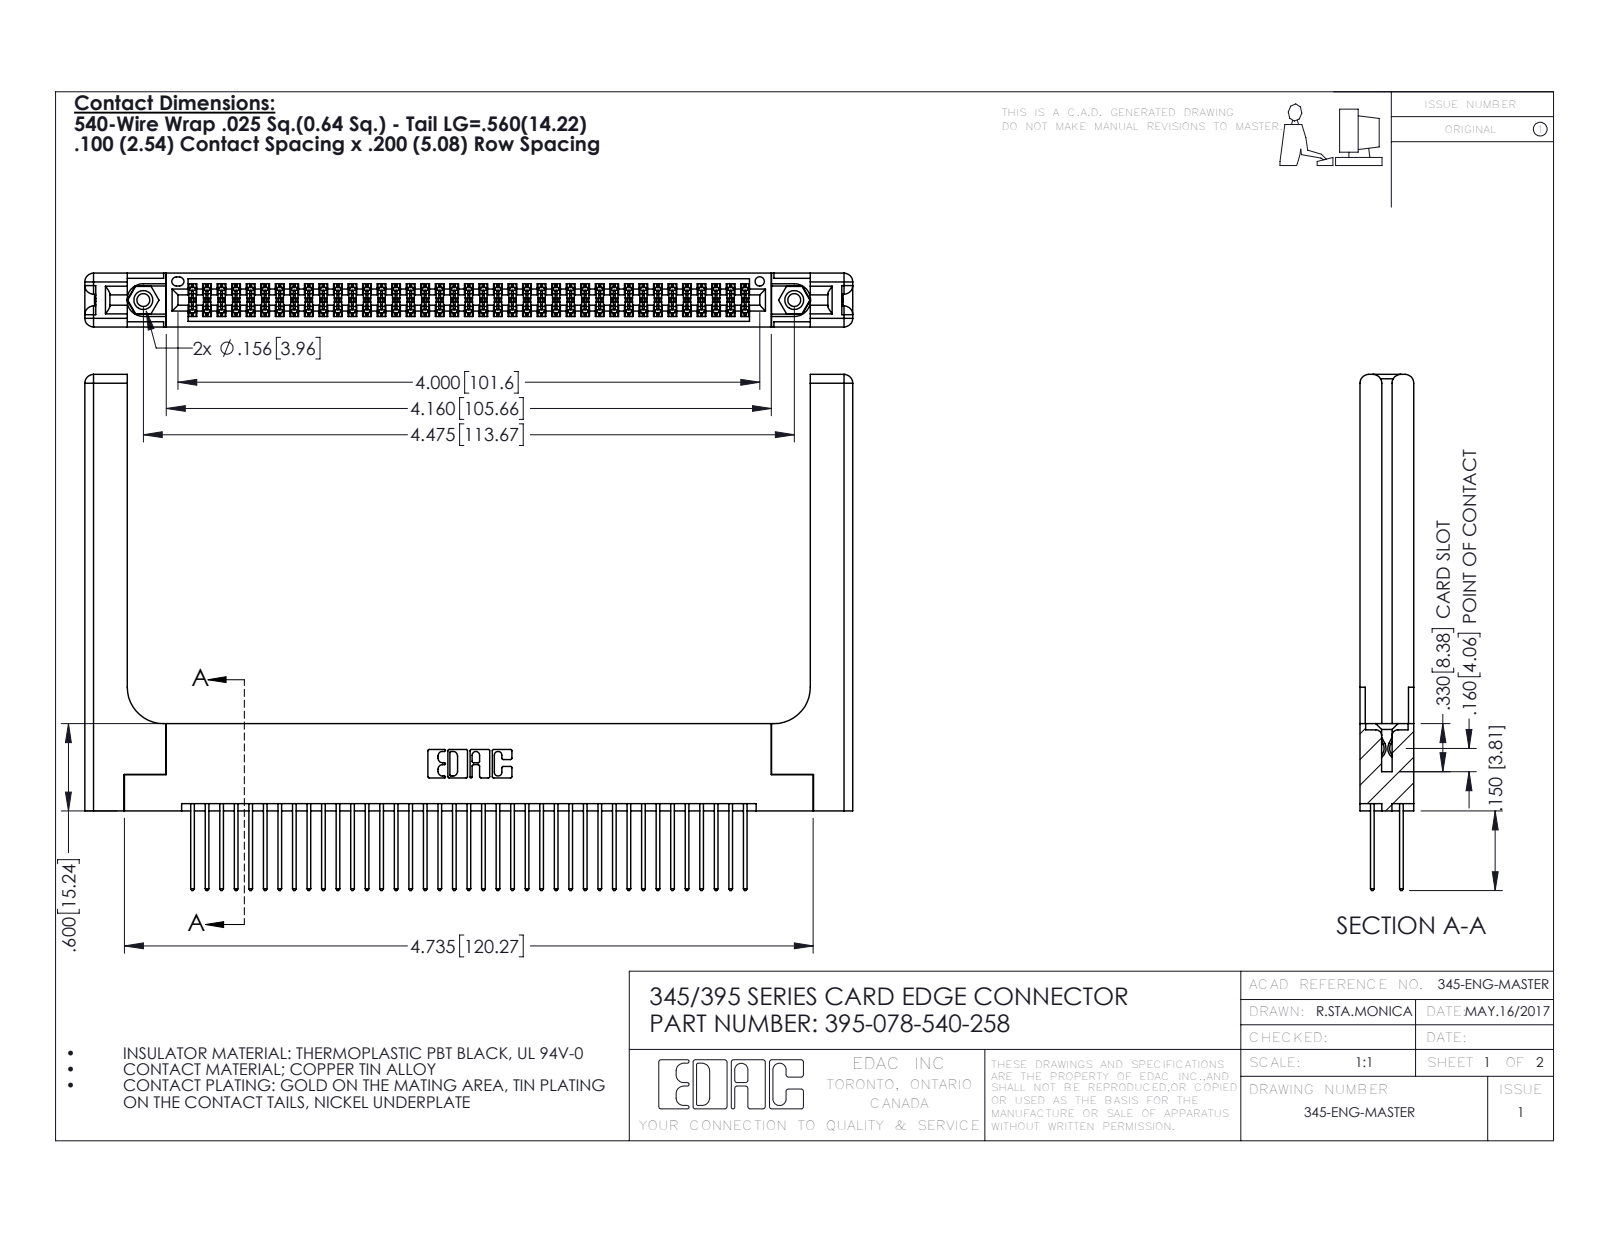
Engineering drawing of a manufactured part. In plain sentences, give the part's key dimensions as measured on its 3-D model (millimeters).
The part is named "345-292-001_345-293-140; 345-220-058_345-220-058; 395-078-540-258; 345-250-001_345-250-001-102 (+1 more)". Its 3-D file was written by "SolidWorks 2016 (CONFIG_CONTROL_DESIGN)". It is 83 solids with 4282 faces: 2802 planar, 1420 cylindrical and 60 other. Overall it measures 134.1 by 90.1 by 9.4 millimeters. Its volume is 21 760 cubic millimeters and its surface area 26 020 square millimeters. Round holes: 2 of diameter 2.3, 2 of diameter 3.2, 2 of diameter 4, 1 of diameter 1.6. Round bosses or shafts: 2 of diameter 3.9. Partial cylindrical surfaces (rounded edges, fillets, slot ends): 117 of radius 0.2, 78 of radius 0.3, 22 of radius 0.3, 16 of radius 1.5, 6 of radius 0.2, 6 of radius 0.8, 3 of radius 0.7, 2 of radius 0.4. The main face-to-face distances are 1.8, 7.6, 9.4, 5.1, 2.5, 6.9, 0.6, 5.7, 4.4, 3.8. The hole center spacings are 6.9, 107.7, 113.7.
